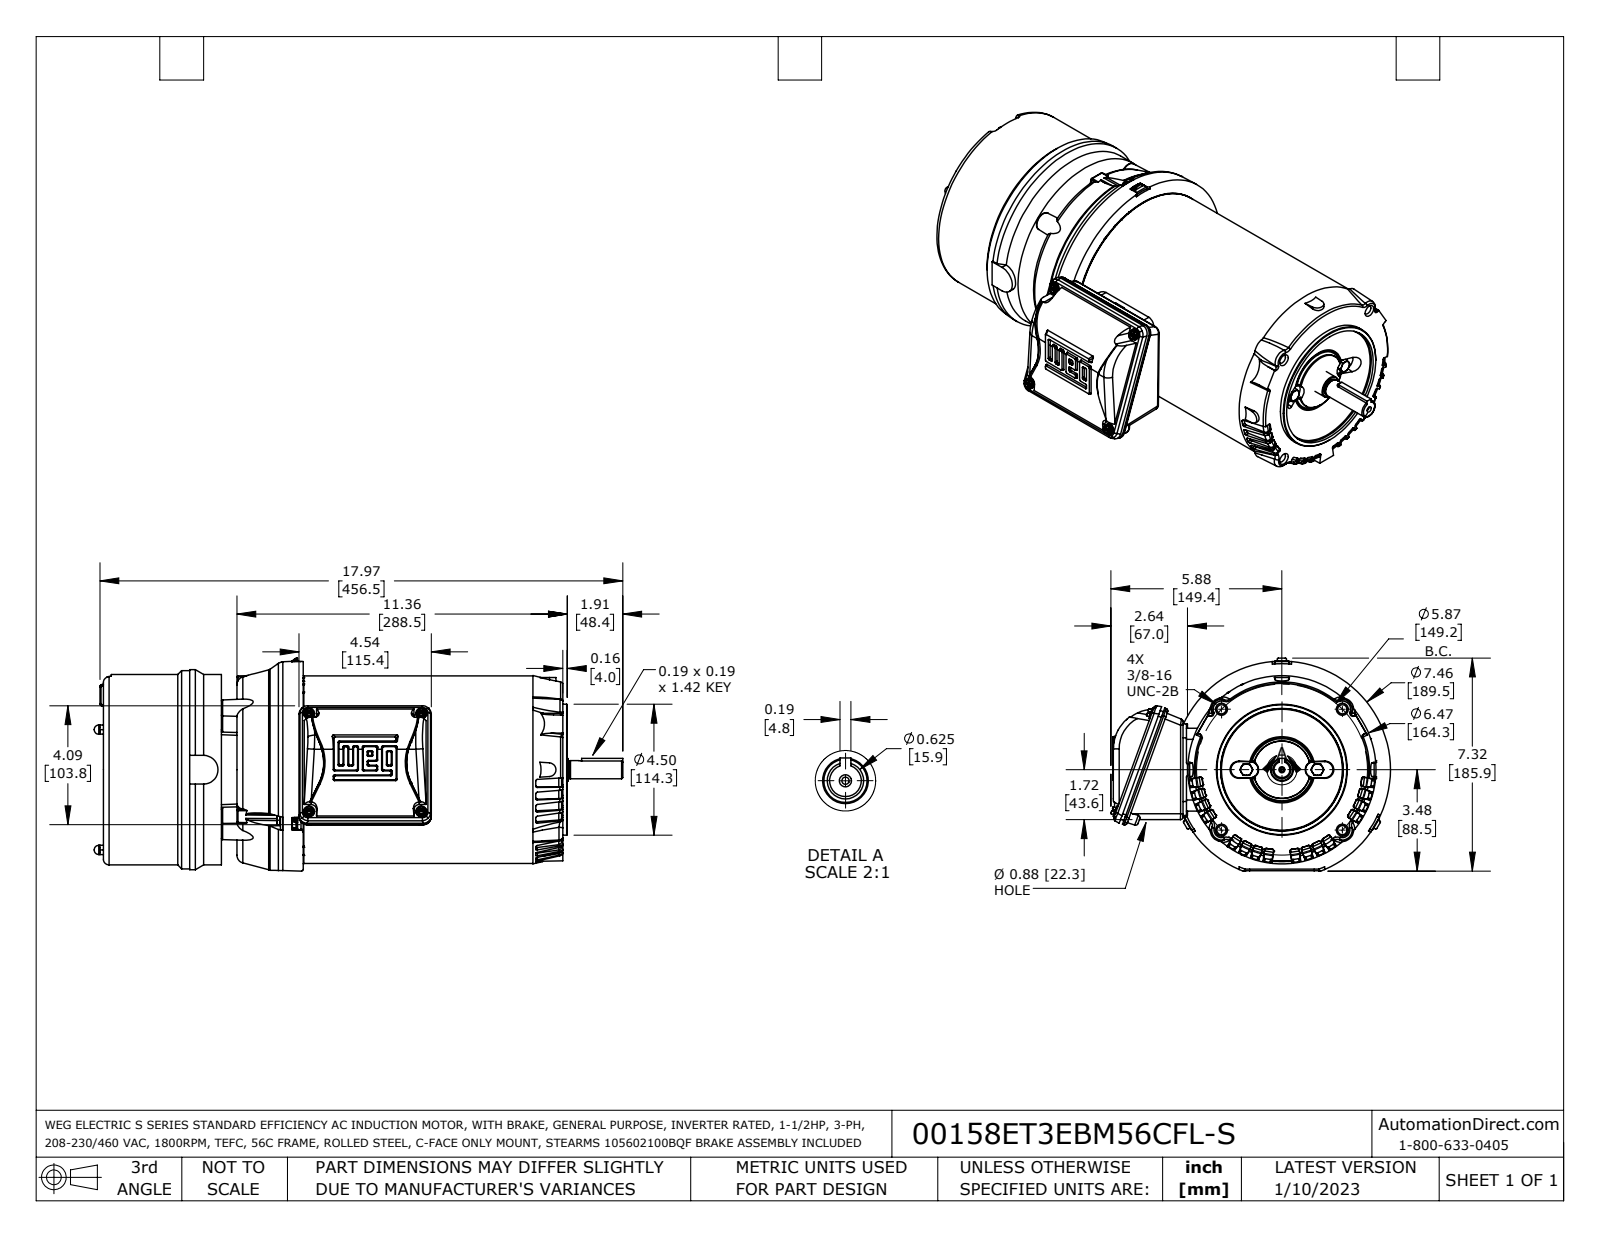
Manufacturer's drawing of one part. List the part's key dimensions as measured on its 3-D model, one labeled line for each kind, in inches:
Part name (STEP PRODUCT): 56C_3PH_TEFC_BM_18165_FL coord fxt
STEP written by: SolidWorks 2021 (AUTOMOTIVE_DESIGN)
Units: inches
Bodies: 15 solids, 1400 faces (530 planar, 350 cylindrical, 520 other)
Overall size (bounding box): 18.169 × 9.612 × 7.319
Volume: 551.6 in³ · Surface area: 772.3 in²
Round holes (diameter × count): ⌀0.313 ×4, ⌀0.124 ×1
Round bosses / shafts (diameter × count): ⌀0.374 ×4, ⌀0.315 ×3, ⌀0.256 ×3, ⌀0.35 ×2, ⌀6.87 ×1, ⌀6.811 ×1, ⌀6.54 ×1, ⌀6.457 ×1
Partial cylindrical surfaces — rounded edges, fillets, slot ends (radius × count): R0.039 ×51, R0.047 ×40, R0.051 ×32, R0.02 ×16, R0.079 ×12, R0.087 ×12, R0.205 ×8, R0.276 ×8
Main face-to-face distances: 7.874, 10.709, 2.835, 4.059, 6.894, 14.768, 4.591, 0.531, 2.303, 10.177
Hole centre spacings: 2.937, 4.154, 5.874
